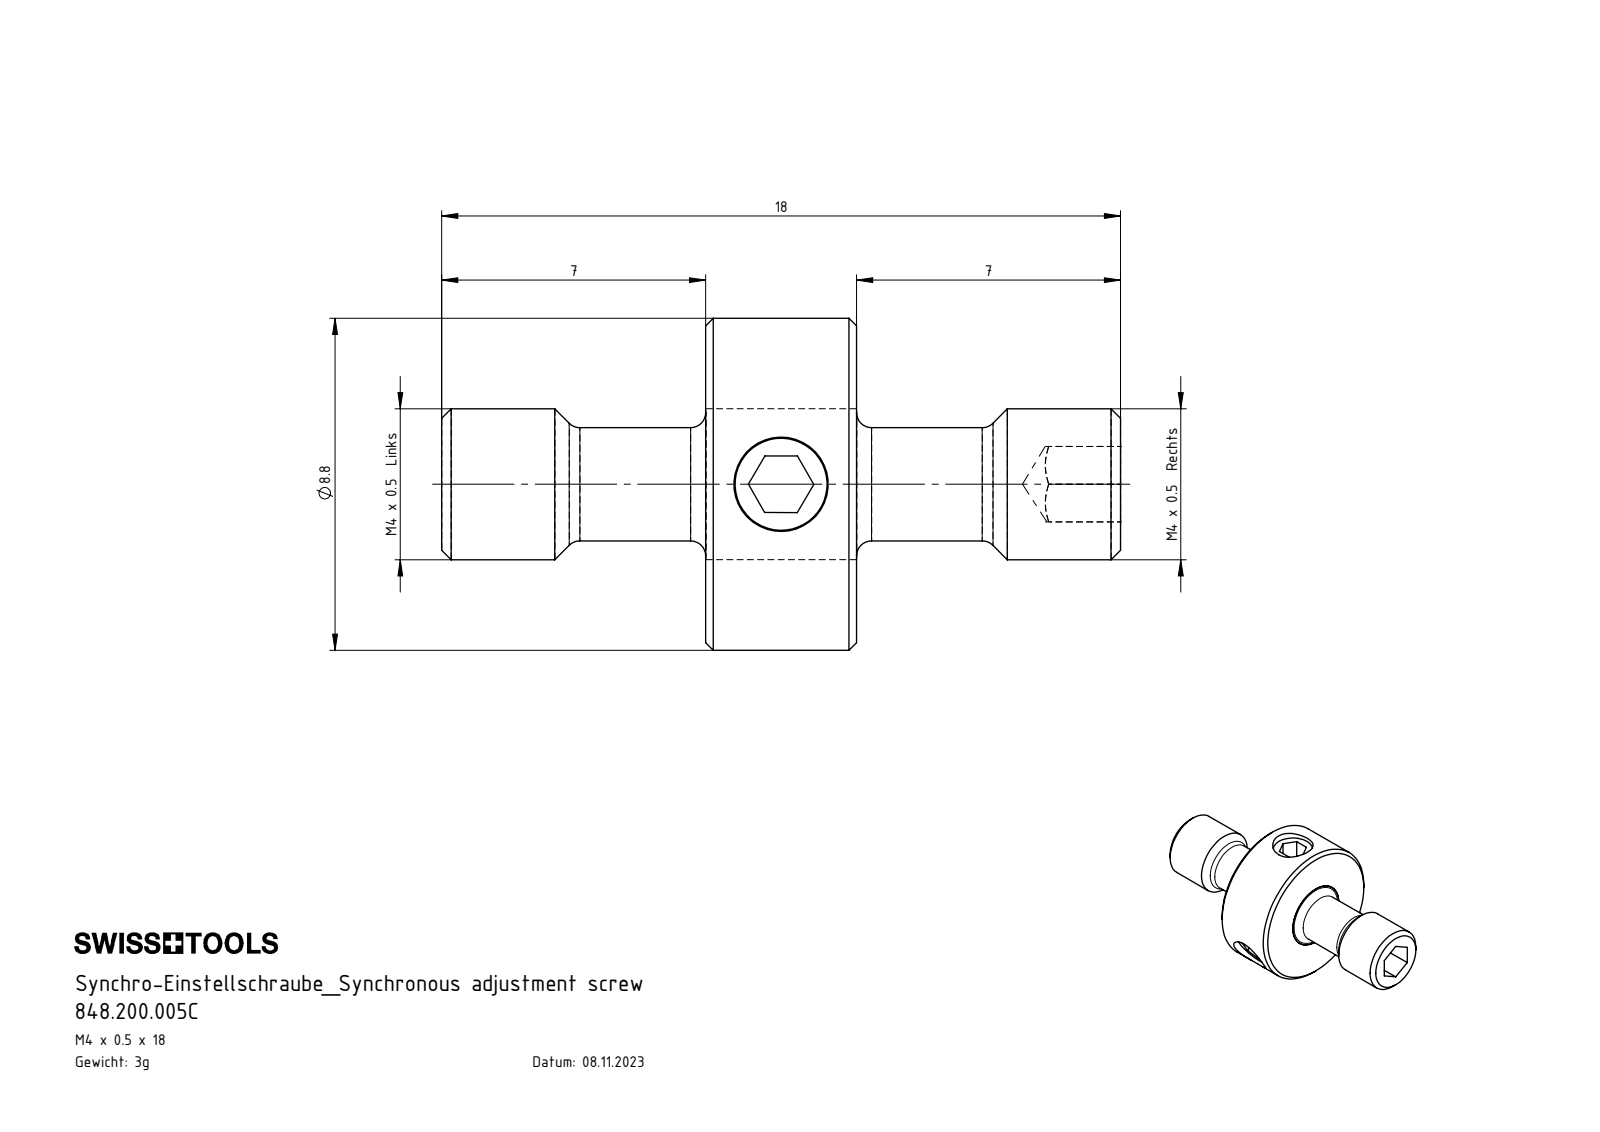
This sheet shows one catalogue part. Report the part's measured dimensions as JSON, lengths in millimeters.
{"part_name": "848.200.005C; ISO 4026 - M3 x 2; Z20-ER3.002.004_A; Z20-ER3.001.018_A", "step_written_by": "SolidWorks 2022 (AUTOMOTIVE_DESIGN)", "units": "millimeters", "bodies": {"solids": 5, "faces": 96, "planar": 36, "cylindrical": 26, "other": 34}, "overall_size": [18, 8.8, 8.8], "volume_mm3": 360, "surface_area_mm2": 636, "round_holes": [[2.5, 3]], "round_bosses_or_shafts": [[3, 4], [8.8, 1], [4, 1]], "face_to_face_distances": [4, 7, 11, 1.5, 2, 18]}
